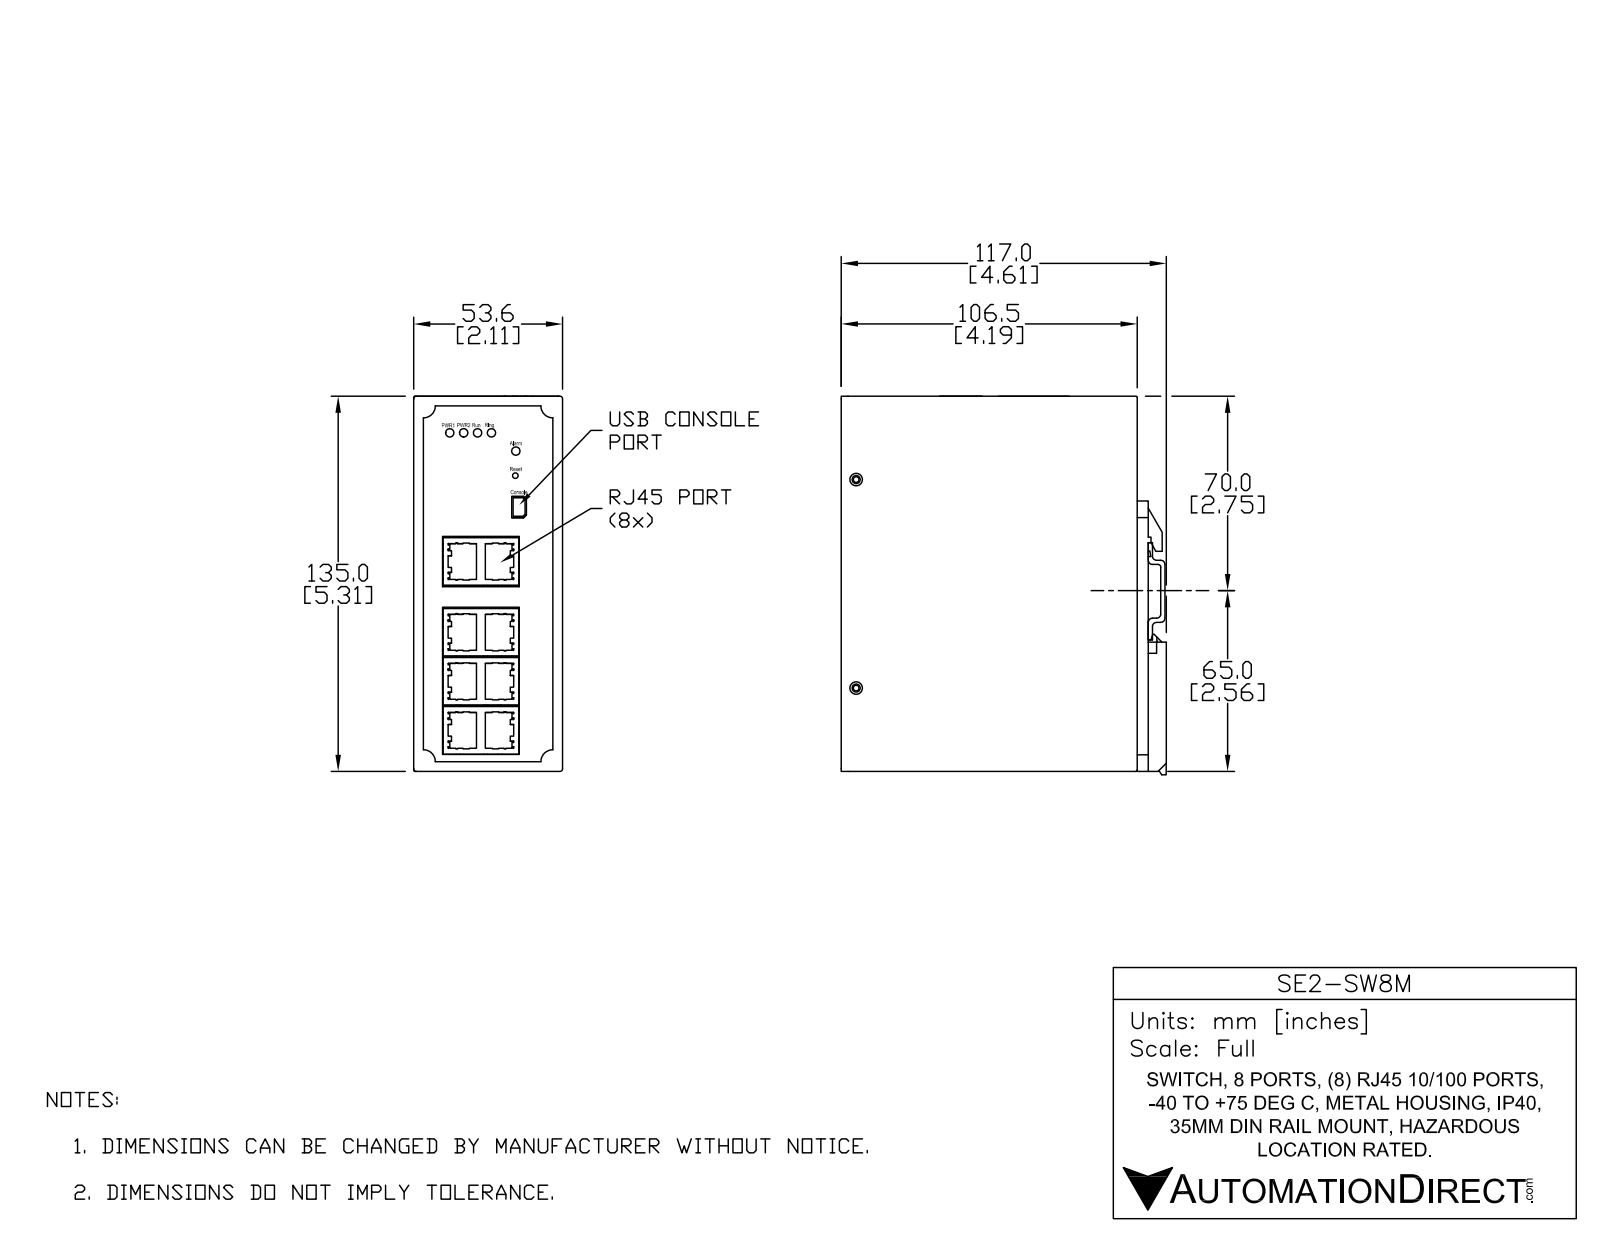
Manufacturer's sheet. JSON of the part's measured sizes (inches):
{"part_name": "SE2-SW8M", "step_written_by": "SolidWorks 2021 (AUTOMOTIVE_DESIGN)", "units": "inches", "bodies": {"solids": 2, "faces": 1132, "planar": 785, "cylindrical": 83, "other": 264}, "overall_size": [5.316, 4.626, 2.126], "volume_in3": 47.73, "surface_area_in2": 103.1, "round_holes": [[0.177, 5]], "round_bosses_or_shafts": [[0.276, 4], [0.22, 4], [0.217, 2]], "partial_cylinders_radius": [[0.01, 24], [0.025, 24], [0.039, 4], [0.096, 4], [0.197, 4], [0.169, 3], [0.079, 2], [0.157, 2]], "face_to_face_distances": [2.11, 5.315, 4.354, 0.177, 4.177, 0.016, 4.37, 0.433, 4.193, 3.973], "hole_center_spacings": [0.976, 1.327, 1.594, 2.161, 1.122, 1.417]}
